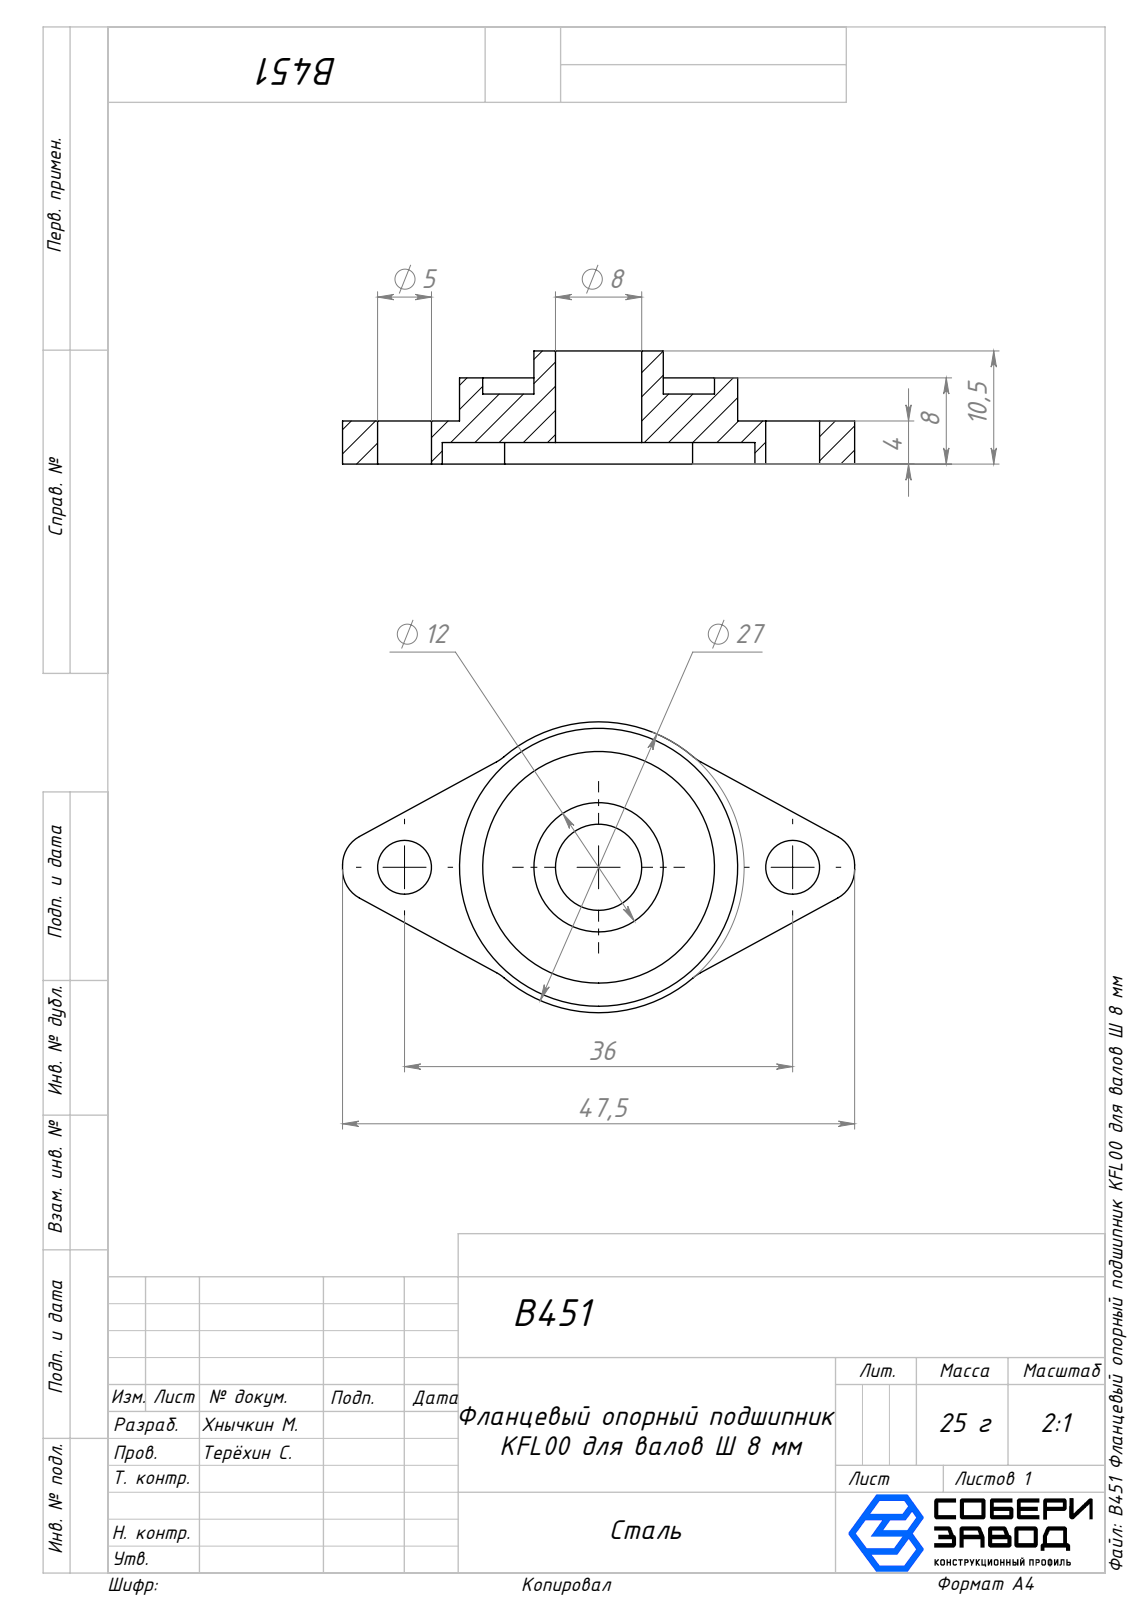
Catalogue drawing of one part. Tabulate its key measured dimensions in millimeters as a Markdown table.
| quantity | value |
| --- | --- |
| part name | B451 Фланцевый опорный подшипник KFL00 для валов Ø 8 мм |
| STEP written by | SolidWorks 2025 (AUTOMOTIVE_DESIGN) |
| units | millimeters |
| bodies | 1 solid, 44 faces (18 planar, 26 cylindrical, 0 other) |
| overall size | 47.5 × 27 × 10.5 |
| volume | 3 615 mm³ |
| surface area | 2 958 mm² |
| round holes (diameter × count) | 5 × 2, 8 × 1, 21.5 × 1 |
| round bosses / shafts (diameter × count) | 25.8 × 1, 12 × 1 |
| partial cylindrical surfaces (radius × count) | 3 × 4, 4 × 4, 11.5 × 1, 13.5 × 1 |
| main face-to-face distances | 2, 4, 6.5, 2.5, 4.5, 8, 6, 1.5, 26.24, 10.5 |
| hole center spacings | 18, 36 |
